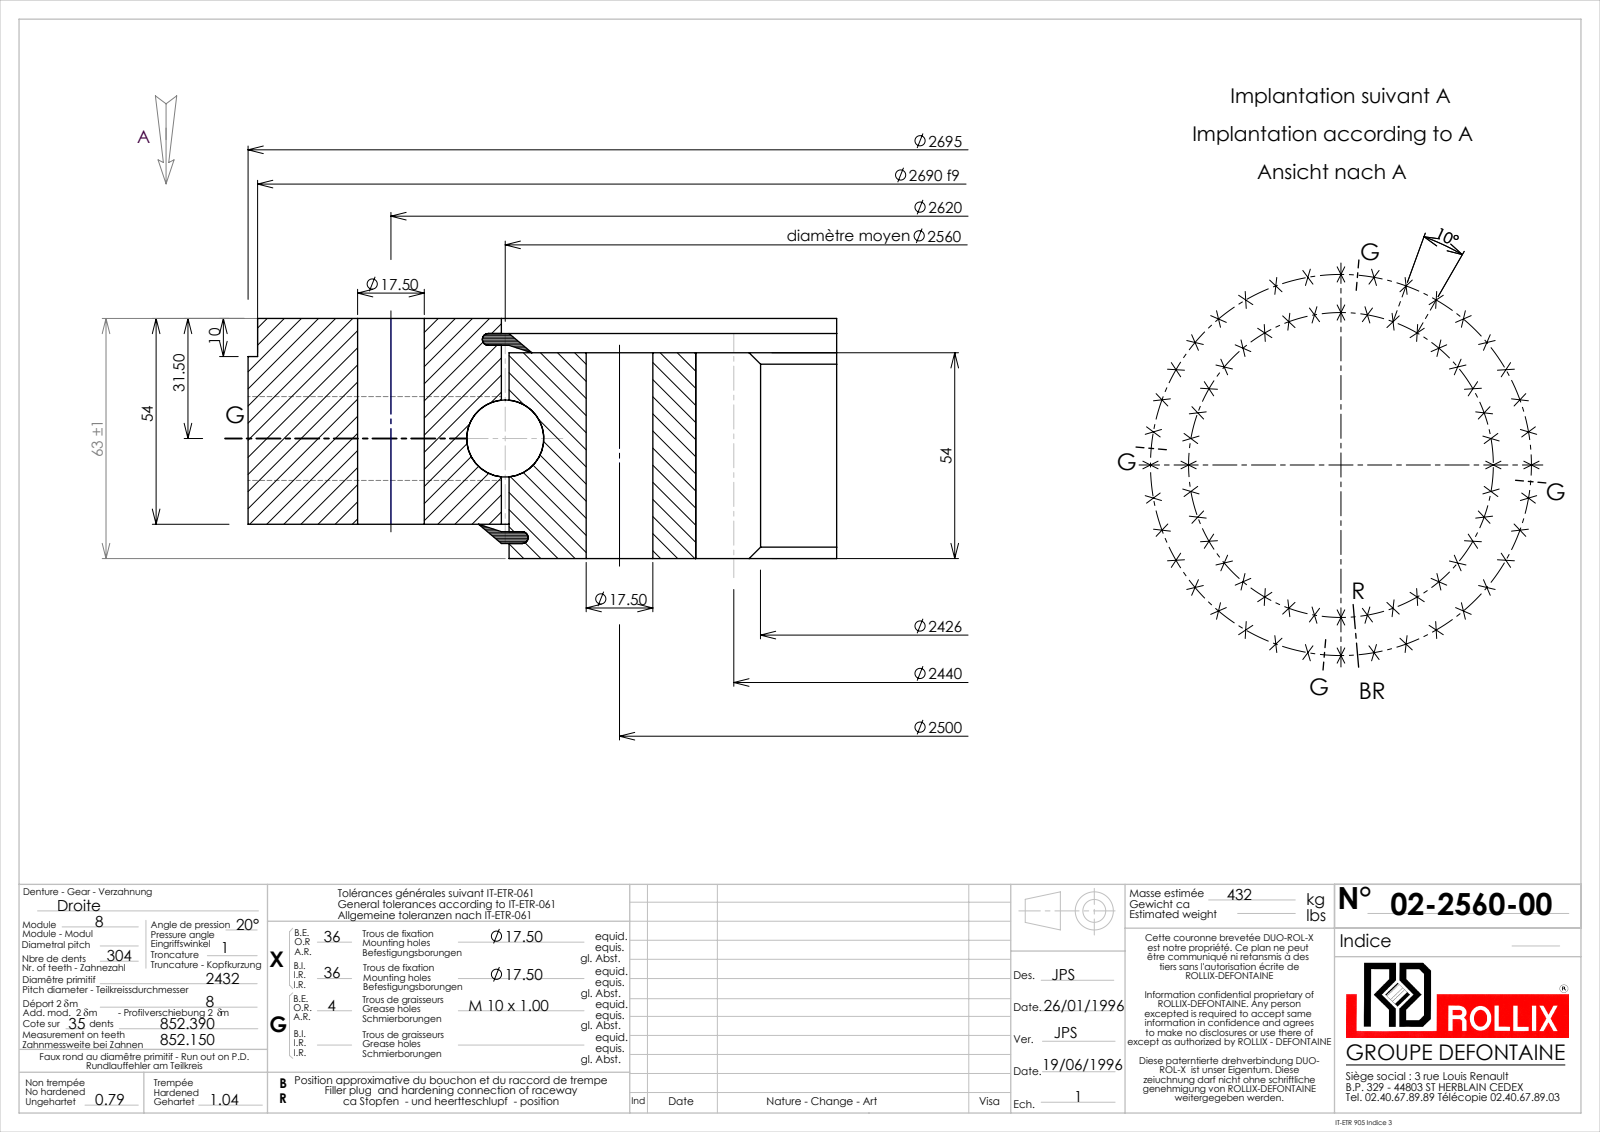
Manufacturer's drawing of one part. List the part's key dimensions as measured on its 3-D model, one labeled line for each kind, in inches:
Part name (STEP PRODUCT): 02-2560-00
STEP written by: SolidWorks 2016 (CONFIG_CONTROL_DESIGN)
Units: inches
Bodies: 5 solids, 2034 faces (621 planar, 777 cylindrical, 636 other)
Overall size (bounding box): 106.102 × 106.102 × 2.48
Volume: 3 121 in³ · Surface area: 7 890 in²
Round holes (diameter × count): ⌀0.689 ×72, ⌀0.354 ×4, ⌀100.867 ×1
Round bosses / shafts (diameter × count): ⌀106.102 ×1, ⌀105.906 ×1, ⌀100.707 ×1
Partial cylindrical surfaces — rounded edges, fillets, slot ends (radius × count): R47.756 ×1, R48.425 ×1
Main face-to-face distances: 2.126, 0.354, 2.48, 1.772, 0.156, 2.325, 0.199, 1.97, 0.278, 2.203
Hole centre spacings: 98.051, 63.267, 25.474, 89.204, 8.578, 49.213, 56.454, 80.625
